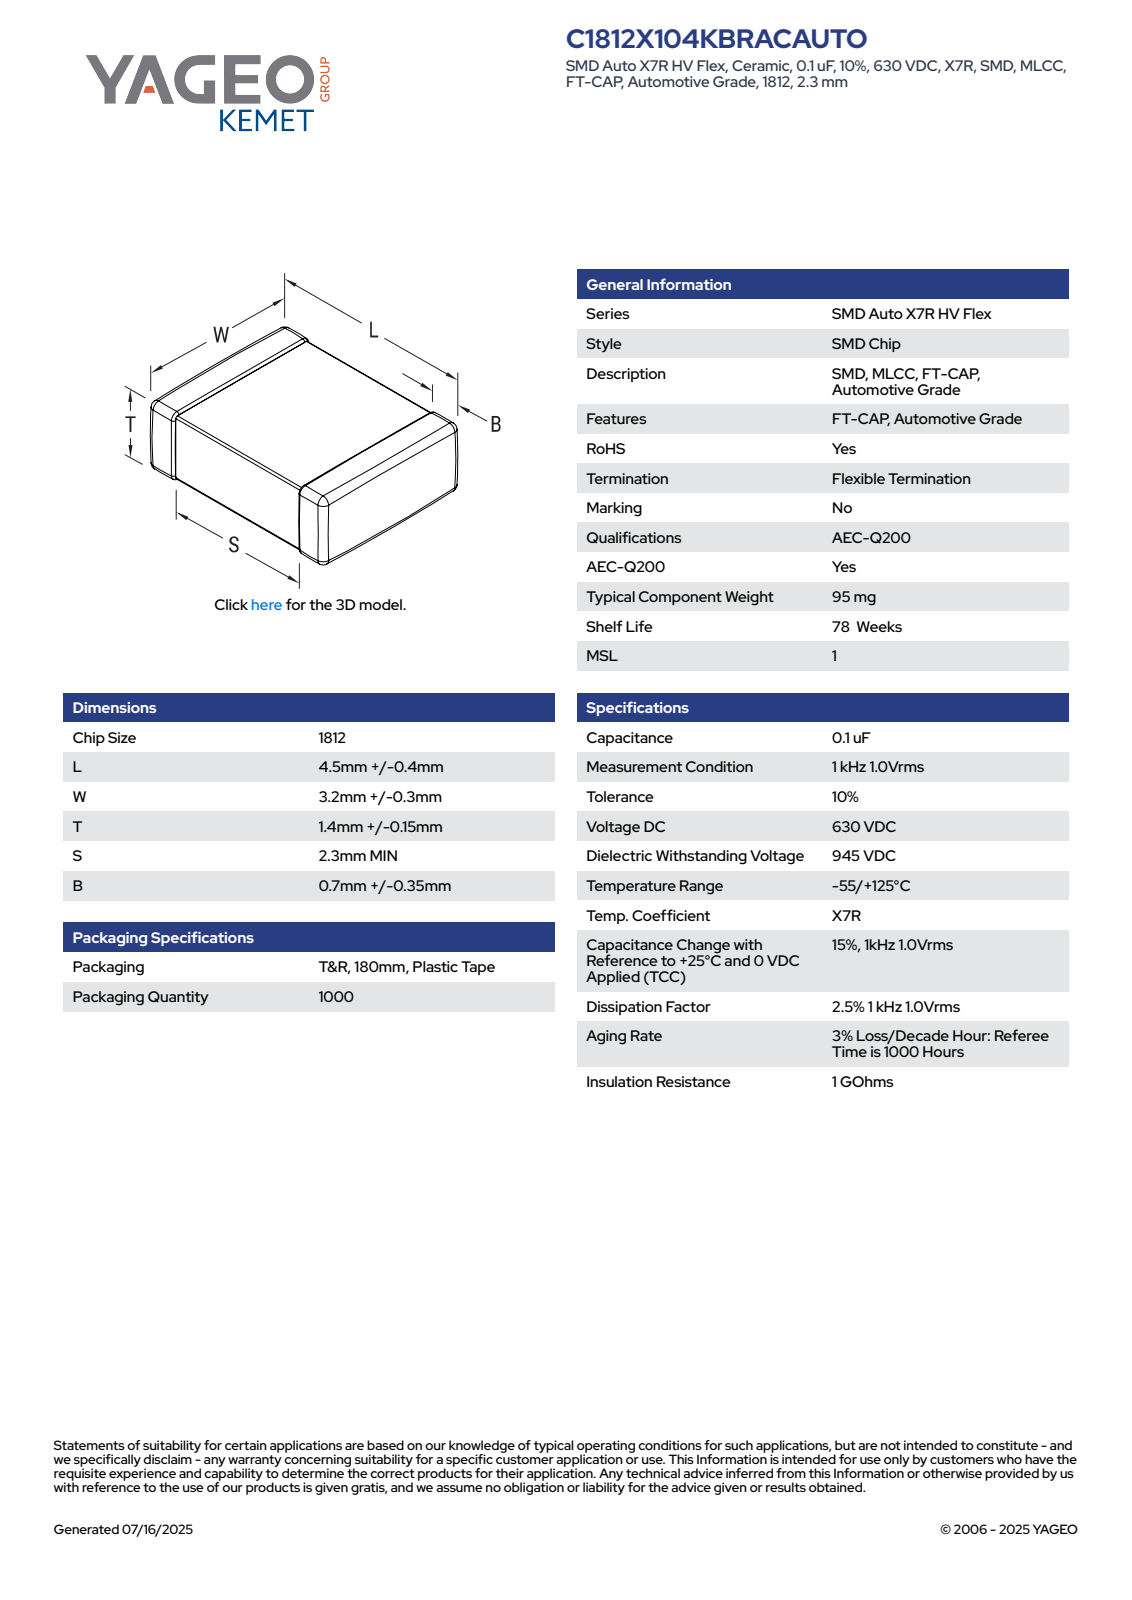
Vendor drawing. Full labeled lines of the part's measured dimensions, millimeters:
Part name (STEP PRODUCT): CCS_CCSTD_1812_L4.9W3.5T1.55B0.7
STEP written by: SolidWorks 2021 (AUTOMOTIVE_DESIGN)
Units: millimetres
Bodies: 4 solids, 125 faces (71 planar, 38 cylindrical, 16 other)
Overall size (bounding box): 4.9 × 3.5 × 1.55
Volume: 25 mm³ · Surface area: 60 mm²
Main face-to-face distances: 1.48, 1.41, 1.55, 3.43, 4.9, 3.36, 3.5, 0.52, 2.25, 2.13
